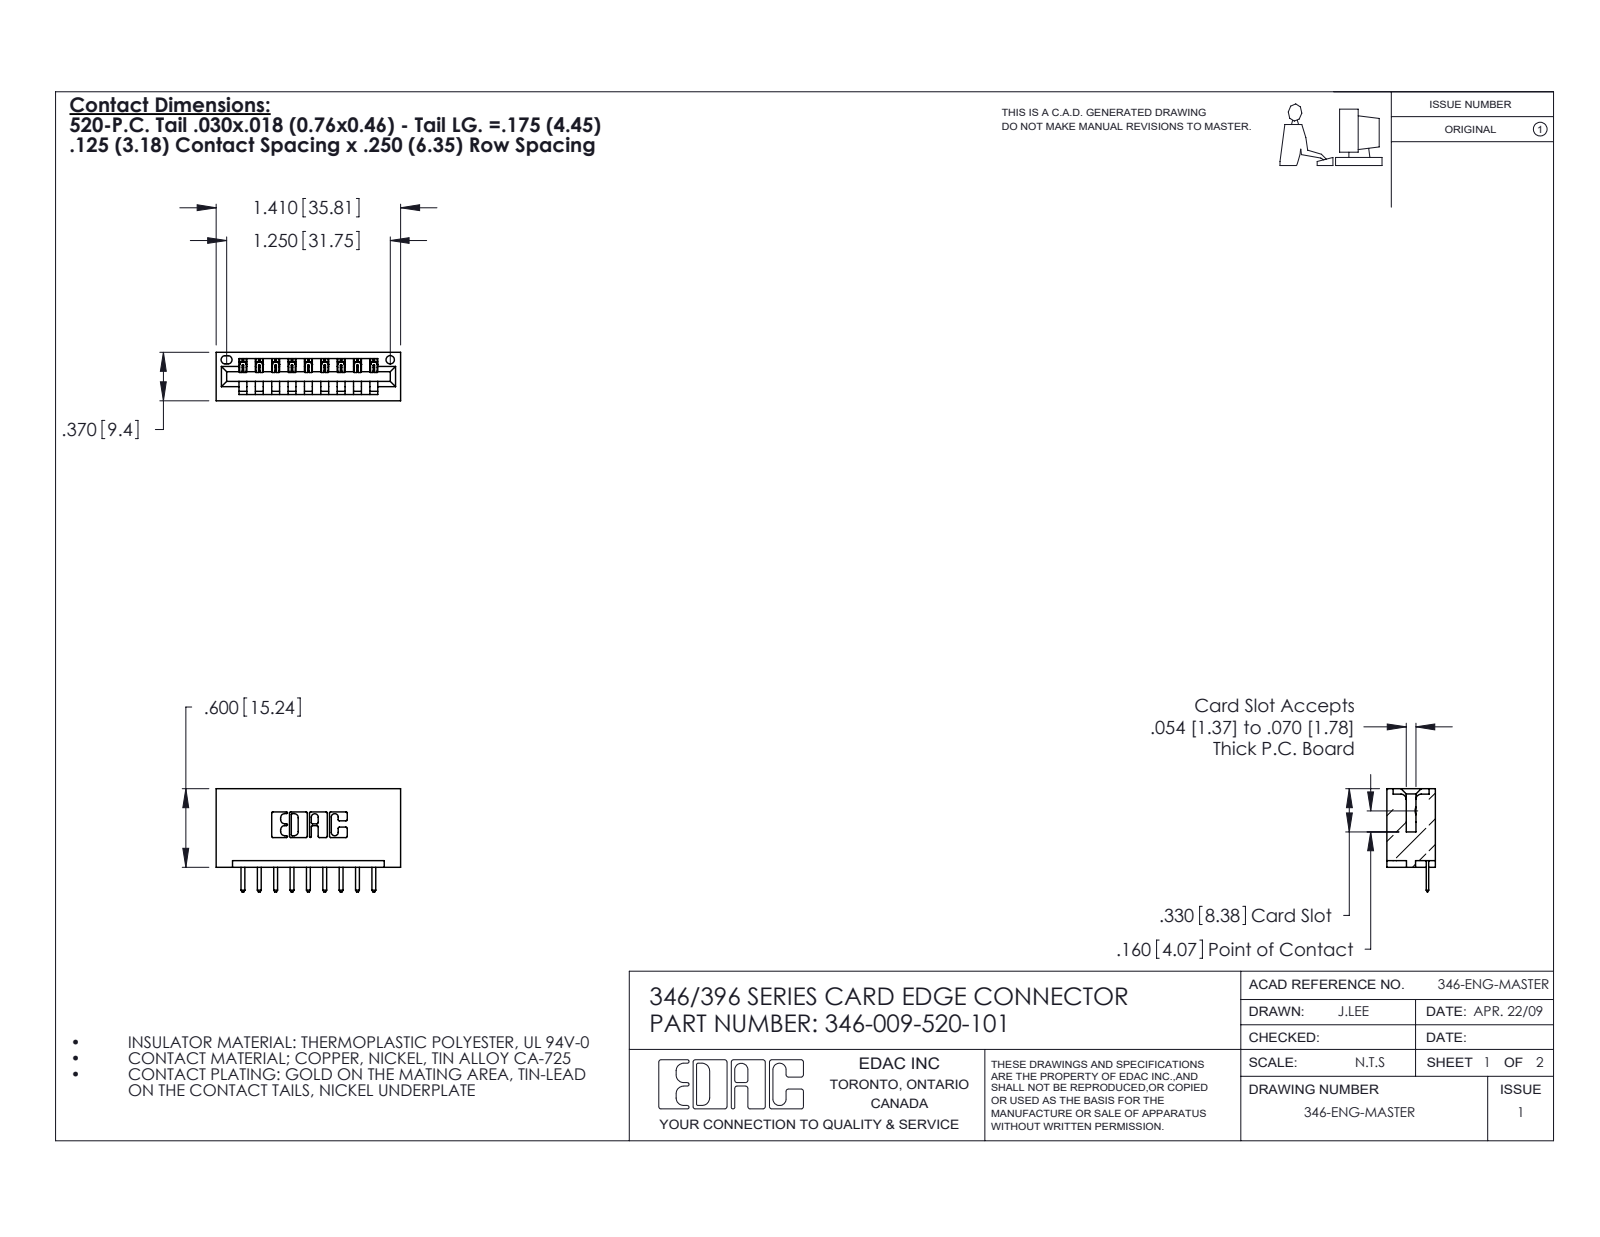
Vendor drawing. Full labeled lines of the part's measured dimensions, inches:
Part name (STEP PRODUCT): 346 Part_No Mounting Lugs; 345-292-001_345-293-120; 346-009-520-101
STEP written by: SolidWorks 2020 (CONFIG_CONTROL_DESIGN)
Units: inches
Bodies: 10 solids, 672 faces (450 planar, 222 cylindrical, 0 other)
Overall size (bounding box): 1.41 × 0.788 × 0.37
Volume: 0.227 in³ · Surface area: 6.646 in²
Round holes (diameter × count): ⌀0.064 ×1
Partial cylindrical surfaces — rounded edges, fillets, slot ends (radius × count): R0.01 ×22, R0.01 ×20, R0.006 ×18, R0.007 ×6, R0.031 ×6, R0.026 ×3, R0.031 ×2, R0.04 ×2
Main face-to-face distances: 0.25, 0.048, 0.322, 0.37, 0.5, 0.125, 0.185, 0.065, 0.125, 0.148
